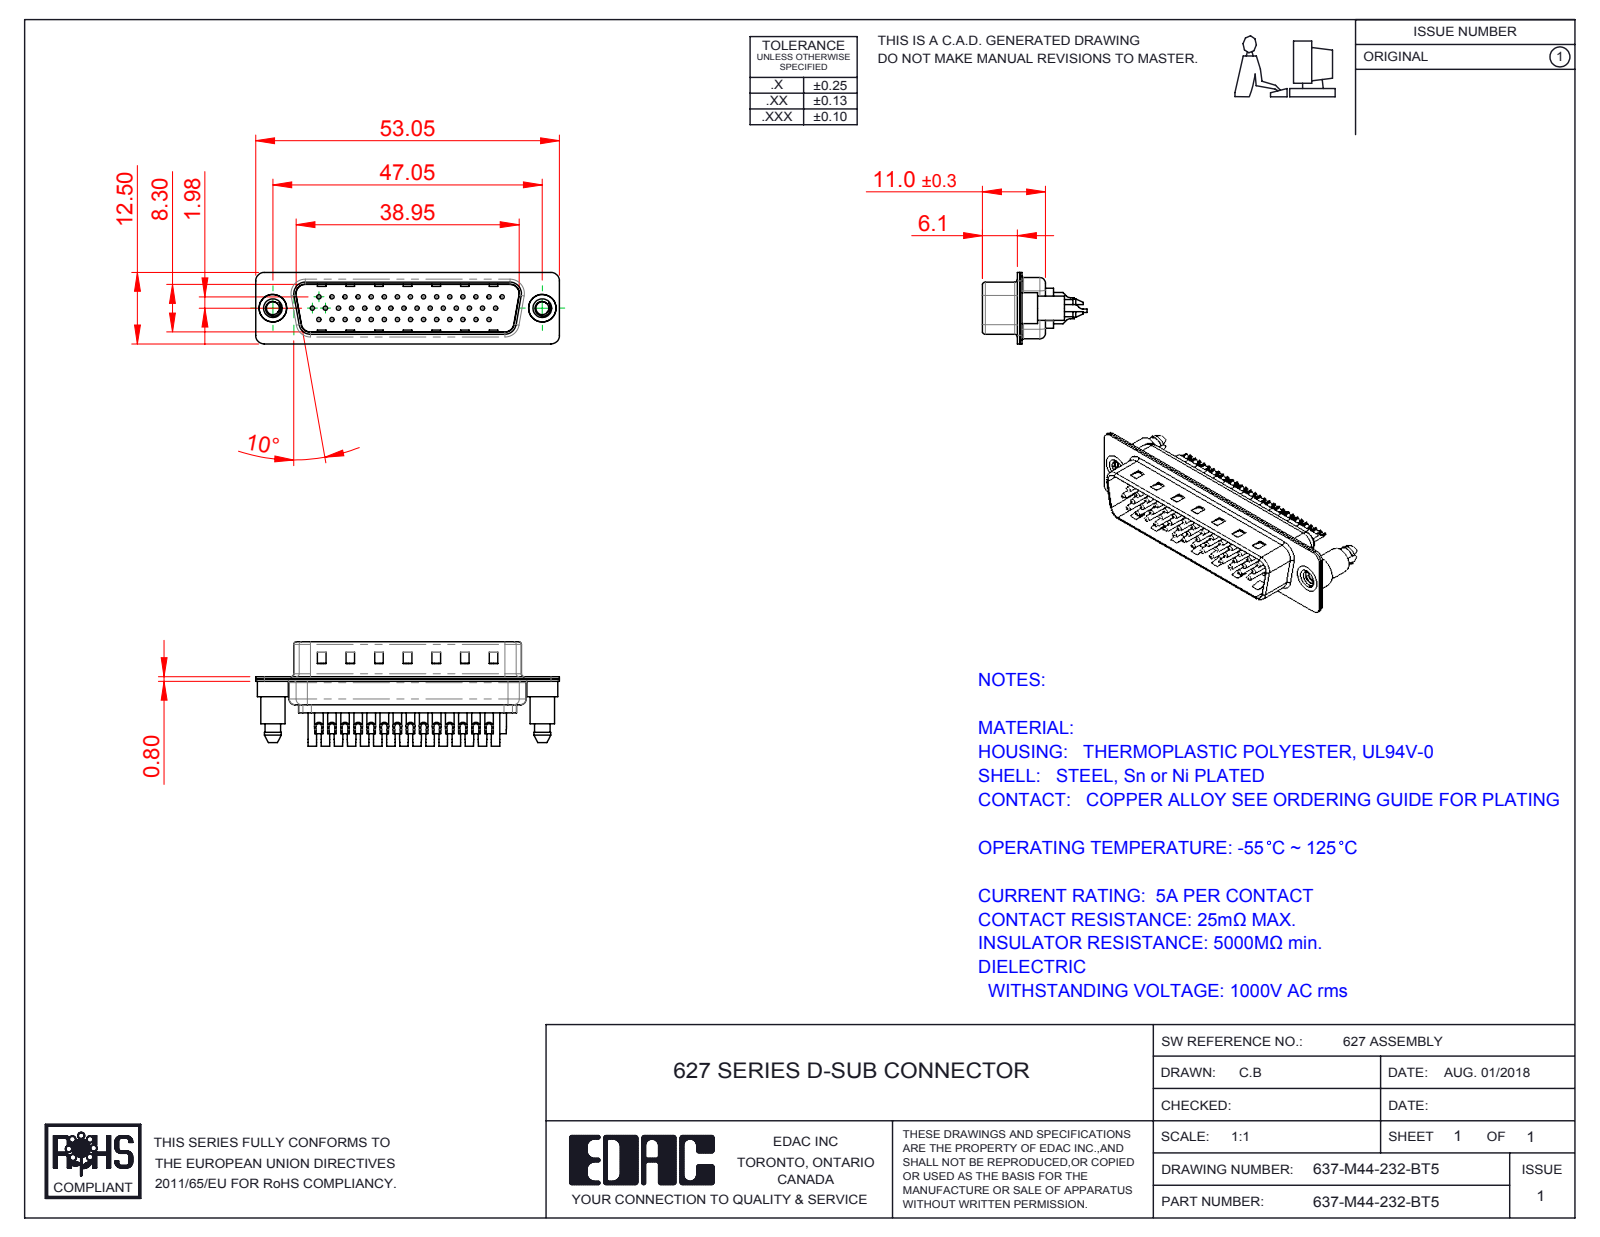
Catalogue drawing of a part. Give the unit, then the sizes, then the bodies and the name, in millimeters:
Units: millimetres
Overall size (bounding box): 53.05 × 18.25 × 12.5
Round holes (diameter × count): ⌀0.75 ×44, ⌀1 ×44, ⌀1.6 ×44, ⌀2 ×44, ⌀2.26 ×2, ⌀4 ×2, ⌀4.8 ×2
Round bosses / shafts (diameter × count): ⌀1.5 ×44, ⌀2 ×3, ⌀0.75 ×3, ⌀5.4 ×2, ⌀4.9 ×2, ⌀4.25 ×2
Partial cylindrical surfaces — rounded edges, fillets, slot ends (radius × count): R1.5 ×18, R2 ×12, R1.6 ×10, R0.5 ×8, R1 ×7, R0.25 ×4, R0.6 ×4, R0.65 ×4
Main face-to-face distances: 0.4, 0.8, 9.5, 9.1, 8.7, 9.9, 0.75, 1.1, 0.35, 1.2
Hole centre spacings: 2.28, 3.96, 2.29, 4.57, 8.24, 6.86, 11.43, 14.99
Volume: 3 108 mm³ · Surface area: 9 343 mm²
Bodies: 49 solids, 2054 faces (583 planar, 873 cylindrical, 598 other)
Part name (STEP PRODUCT): 637M Contact Row 3_32; 637M Contact Row 2_32; 637M Shell Rear_44 Contacts; 637M Housing_44 Contacts (+4 more)
STEP written by: SolidWorks 2016 (CONFIG_CONTROL_DESIGN)
